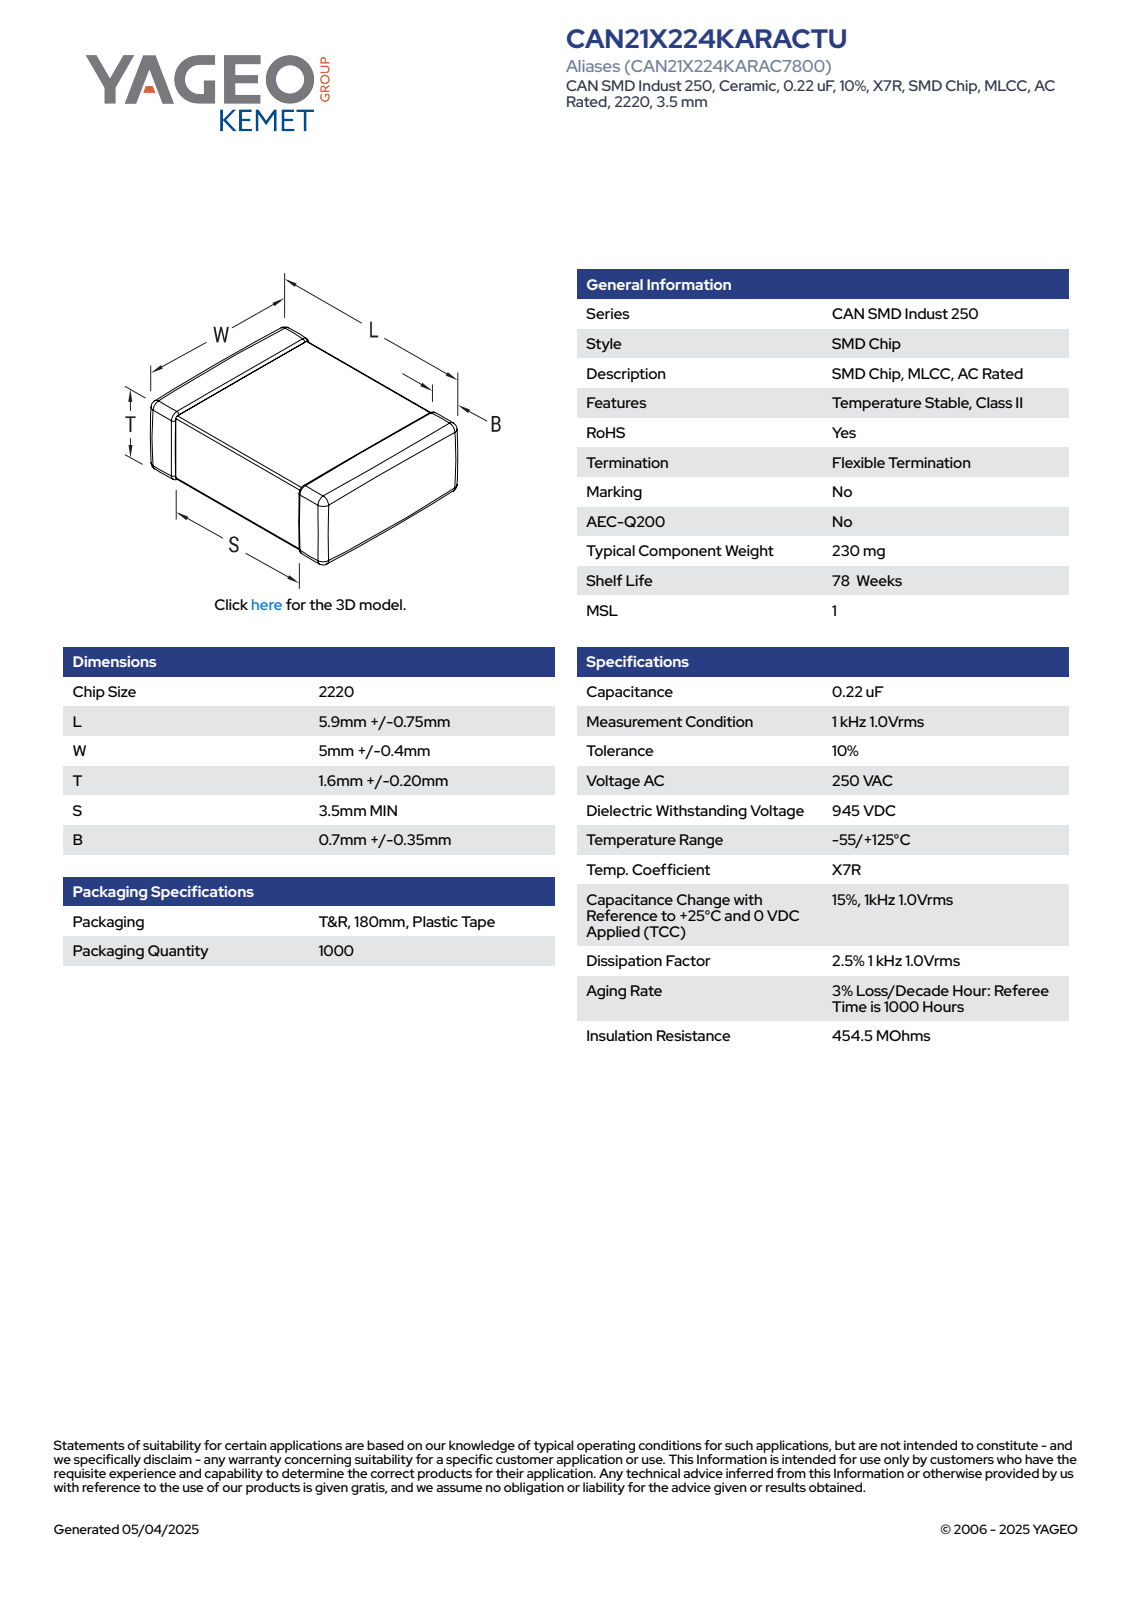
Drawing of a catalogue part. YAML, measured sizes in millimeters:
part_name: "CCS_CCSTD_2220_L6.65W5.4T1.8B0.7"
step_written_by: "SolidWorks 2021 (AUTOMOTIVE_DESIGN)"
units: millimeters
bodies: {solids: 4, faces: 125, planar: 71, cylindrical: 38, other: 16}
overall_size: [6.65, 5.4, 1.8]
volume: 57
surface_area: 114
partial_cylinders:
  - {radius: 0.11, count: 24}
face_to_face_distances: [1.58, 1.69, 1.8, 6.65, 5.18, 5.29, 5.4, 2.8, 3.85, 3.59]
